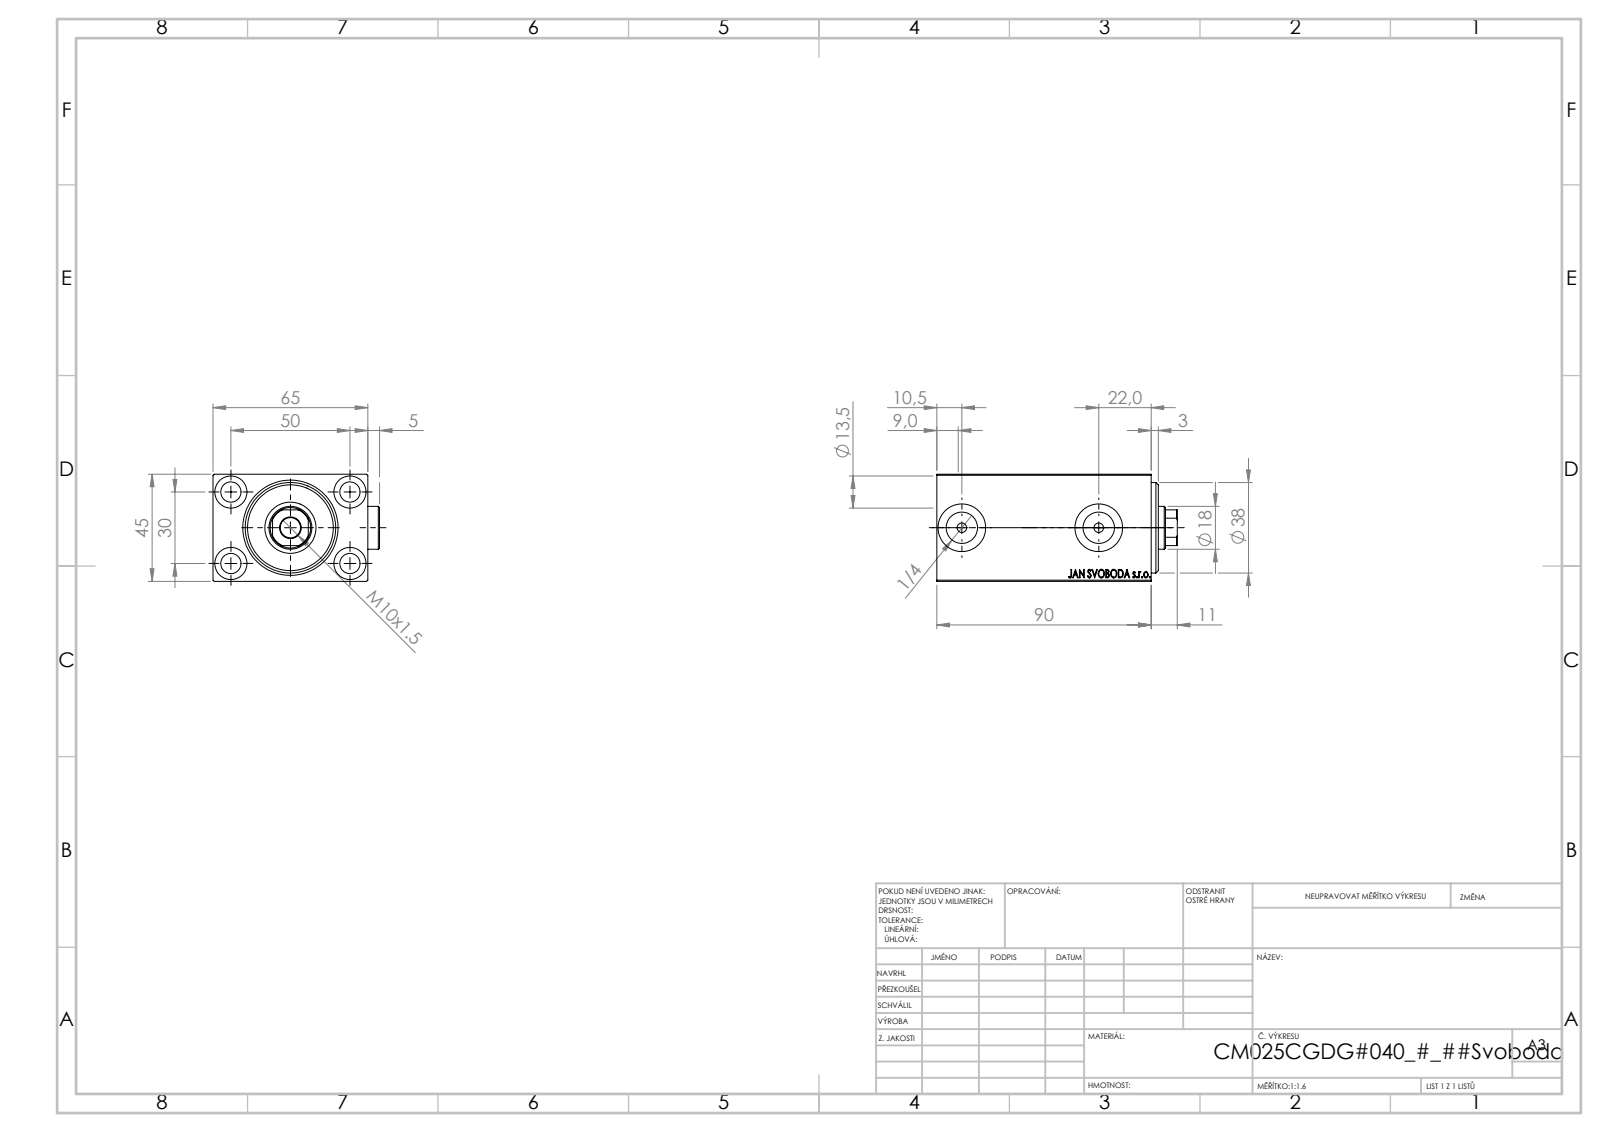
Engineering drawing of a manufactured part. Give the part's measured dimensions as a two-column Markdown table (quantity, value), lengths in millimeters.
| quantity | value |
| --- | --- |
| part name | V450CM_C_Body; V450CM_VC_B; V450CM_C_VCP; Zatka_OIL_PORT |
| STEP written by | SolidWorks 2019 (CONFIG_CONTROL_DESIGN) |
| units | millimeters |
| bodies | 5 solids, 916 faces (442 planar, 76 cylindrical, 398 other) |
| overall size | 101 × 69.9 × 45 |
| volume | 225 856 mm³ |
| surface area | 58 249 mm² |
| round holes (diameter × count) | 8.5 × 5, 13.5 × 4, 4 × 2, 13.16 × 2, 20 × 2, 18 × 1, 21.5 × 1, 25 × 1, 27 × 1, 38 × 1 |
| round bosses / shafts (diameter × count) | 18 × 2 |
| partial cylindrical surfaces (radius × count) | 8.5 × 1 |
| main face-to-face distances | 45, 65, 5, 6, 79, 84, 64.9, 85, 90, 3 |
| hole center spacings | 29.15, 30, 50, 58.31, 57.5 |
